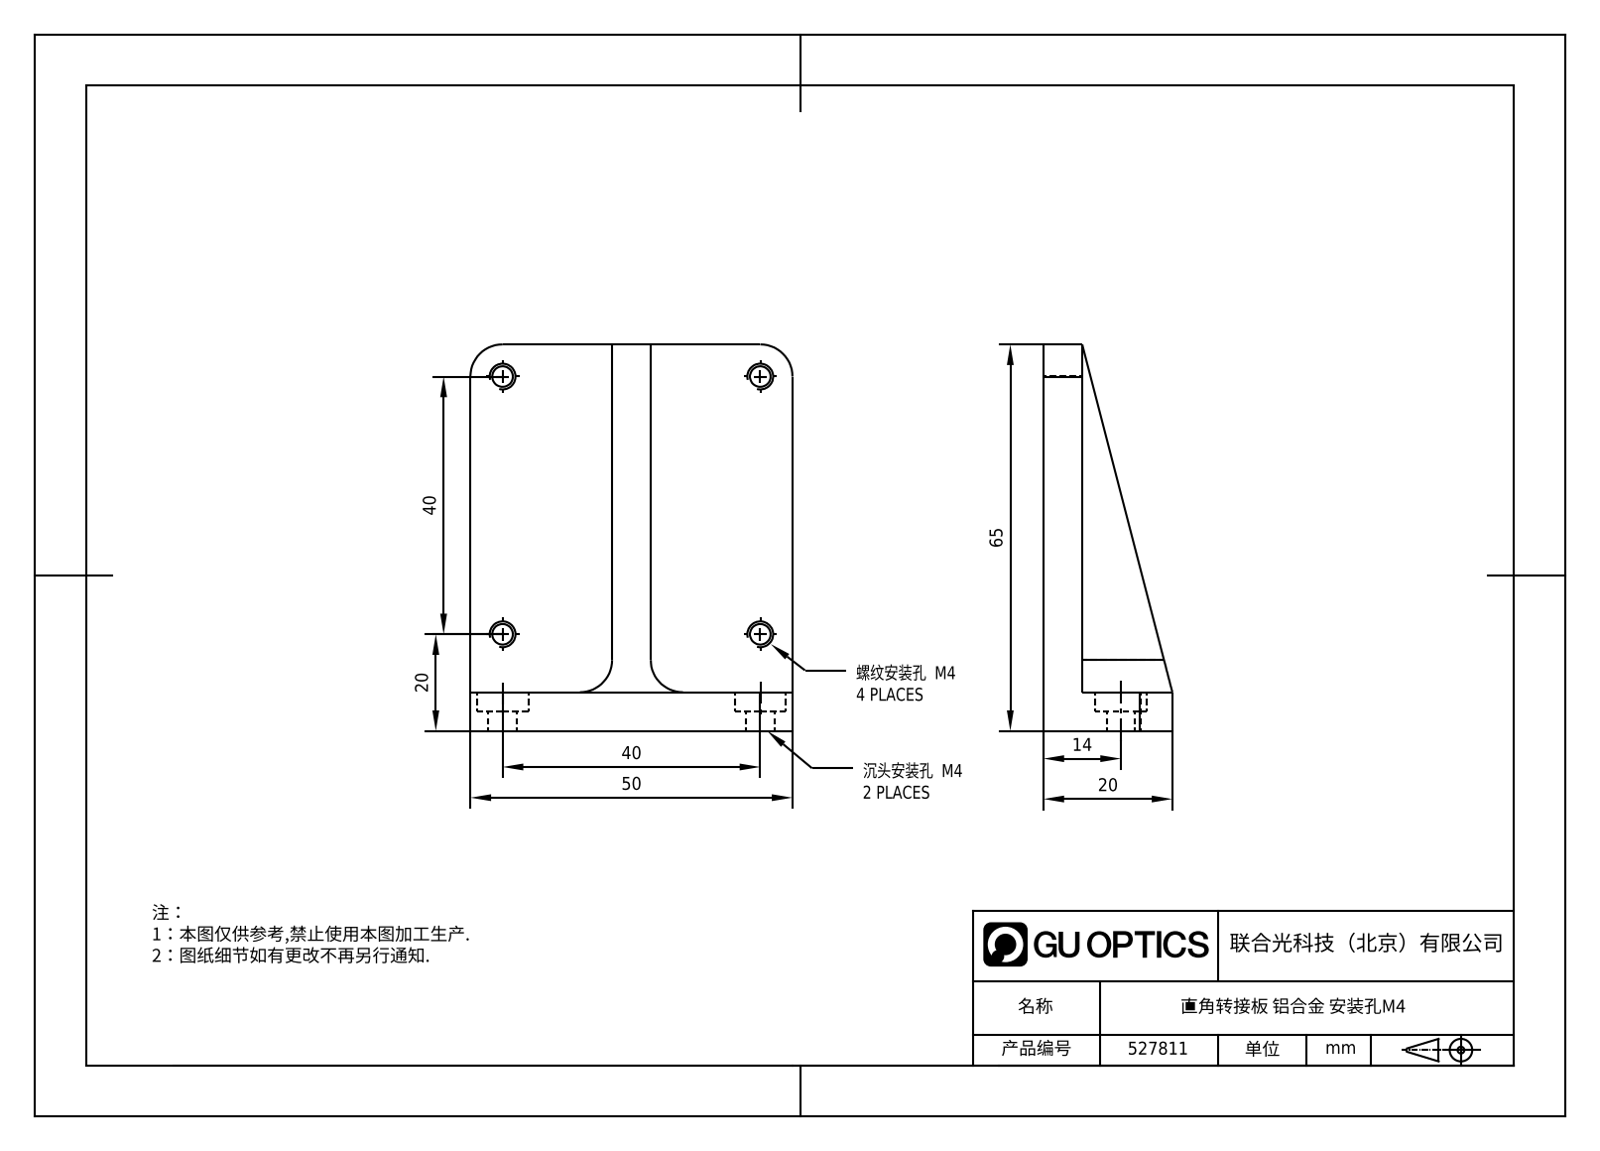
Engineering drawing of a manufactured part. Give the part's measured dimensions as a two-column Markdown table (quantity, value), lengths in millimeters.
| quantity | value |
| --- | --- |
| part name | 1.6.9.3_ZSJ-Z050_50mm直角转接板，带M4螺孔和M4沉头孔 |
| STEP written by | SolidWorks 2021 (CONFIG_CONTROL_DESIGN) |
| units | millimeters |
| bodies | 1 solid, 37 faces (15 planar, 22 cylindrical, 0 other) |
| overall size | 65 × 50 × 20 |
| volume | 25 594 mm³ |
| surface area | 10 397 mm² |
| round holes (diameter × count) | 3.3 × 4, 4.5 × 2, 8 × 2 |
| partial cylindrical surfaces (radius × count) | 5 × 6 |
| main face-to-face distances | 6, 22, 28, 50, 65, 59, 20, 14, 3, 62 |
| hole center spacings | 40, 56.57 |
